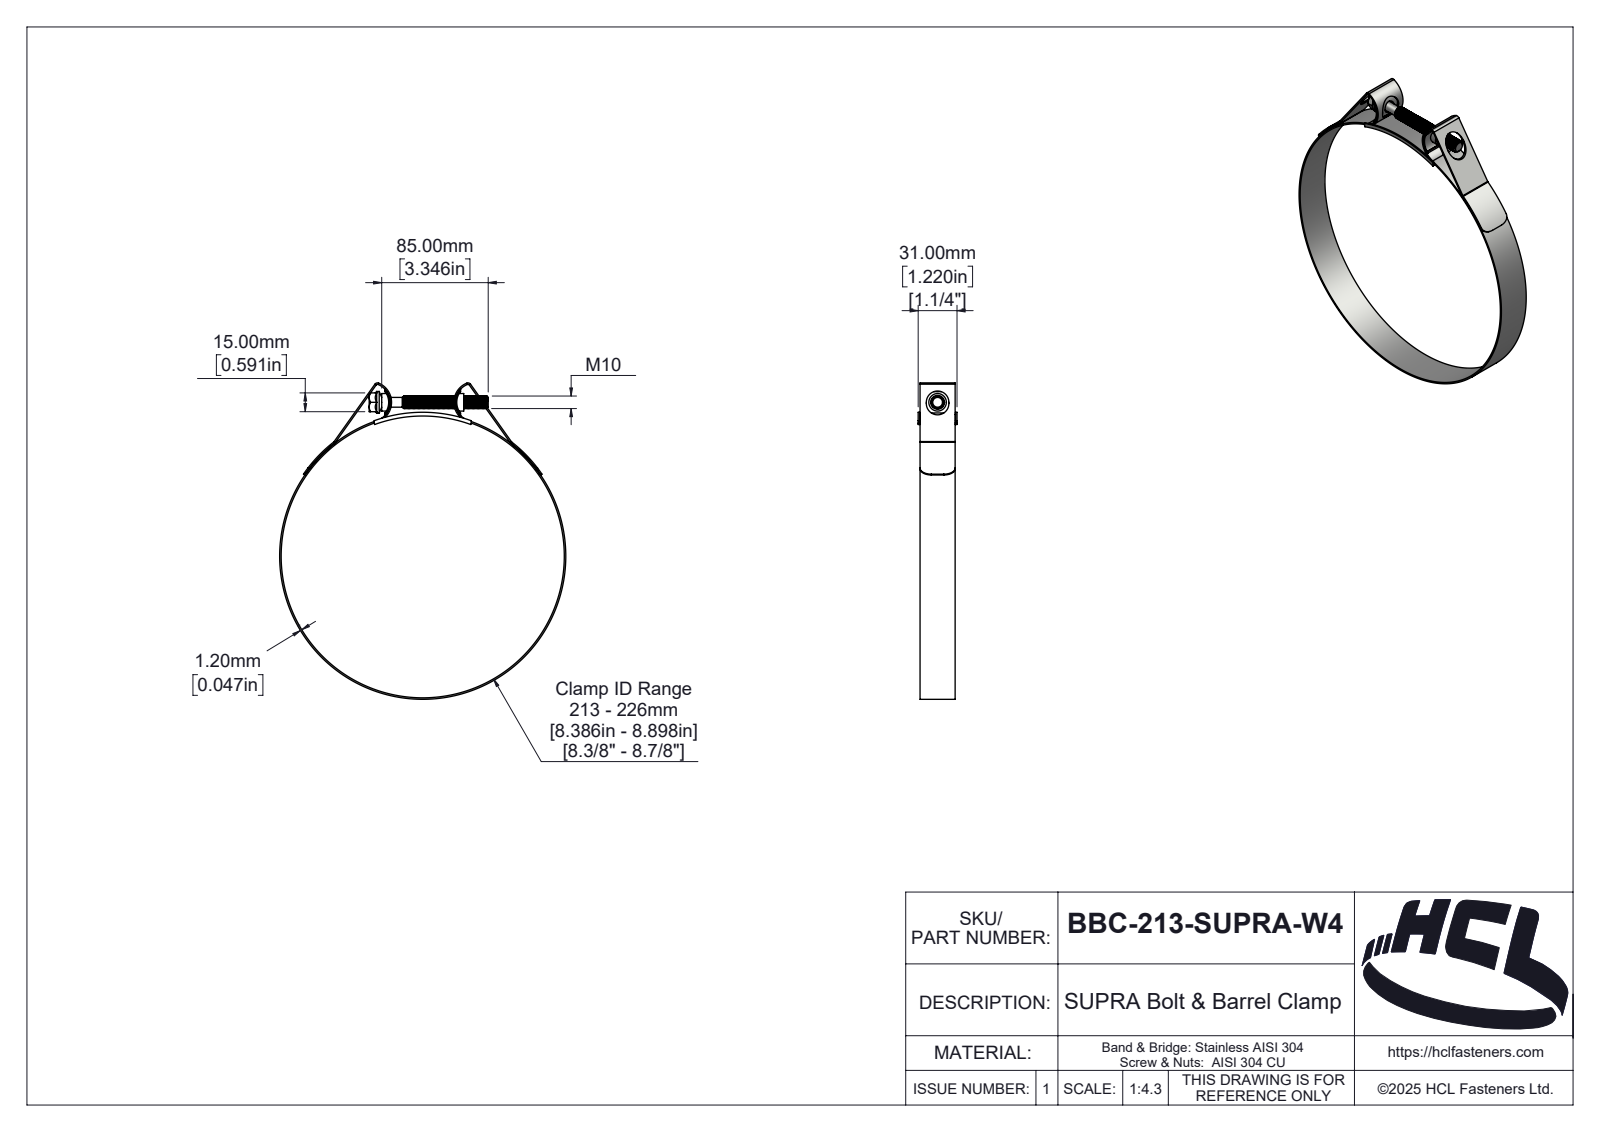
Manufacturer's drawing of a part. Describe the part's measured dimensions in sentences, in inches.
The part is named "BBC-213-SUPRA-W4". Its 3-D file was written by "SolidWorks 2025 (AUTOMOTIVE_DESIGN)". It is 5 solids with 383 faces: 50 planar, 246 cylindrical and 87 other. Overall it measures 9.939 by 8.992 by 1.22 inches. Its volume is 2.528 cubic inches and its surface area 99.32 square inches. Round holes: 1 of diameter 8.898. Round bosses or shafts: 1 of diameter 8.992, 1 of diameter 0.682, 1 of diameter 0.551, 1 of diameter 0.394, 1 of diameter 0.307. Partial cylindrical surfaces (rounded edges, fillets, slot ends): 4 of radius 0.039, 2 of radius 0.051, 2 of radius 0.079, 2 of radius 0.098, 2 of radius 0.126, 2 of radius 0.354, 2 of radius 0.561, 2 of radius 0.6. The main face-to-face distances are 0.047, 1.102, 0.059, 1.161, 1.173, 1.114, 1.22, 1.126, 0.591, 0.098.
